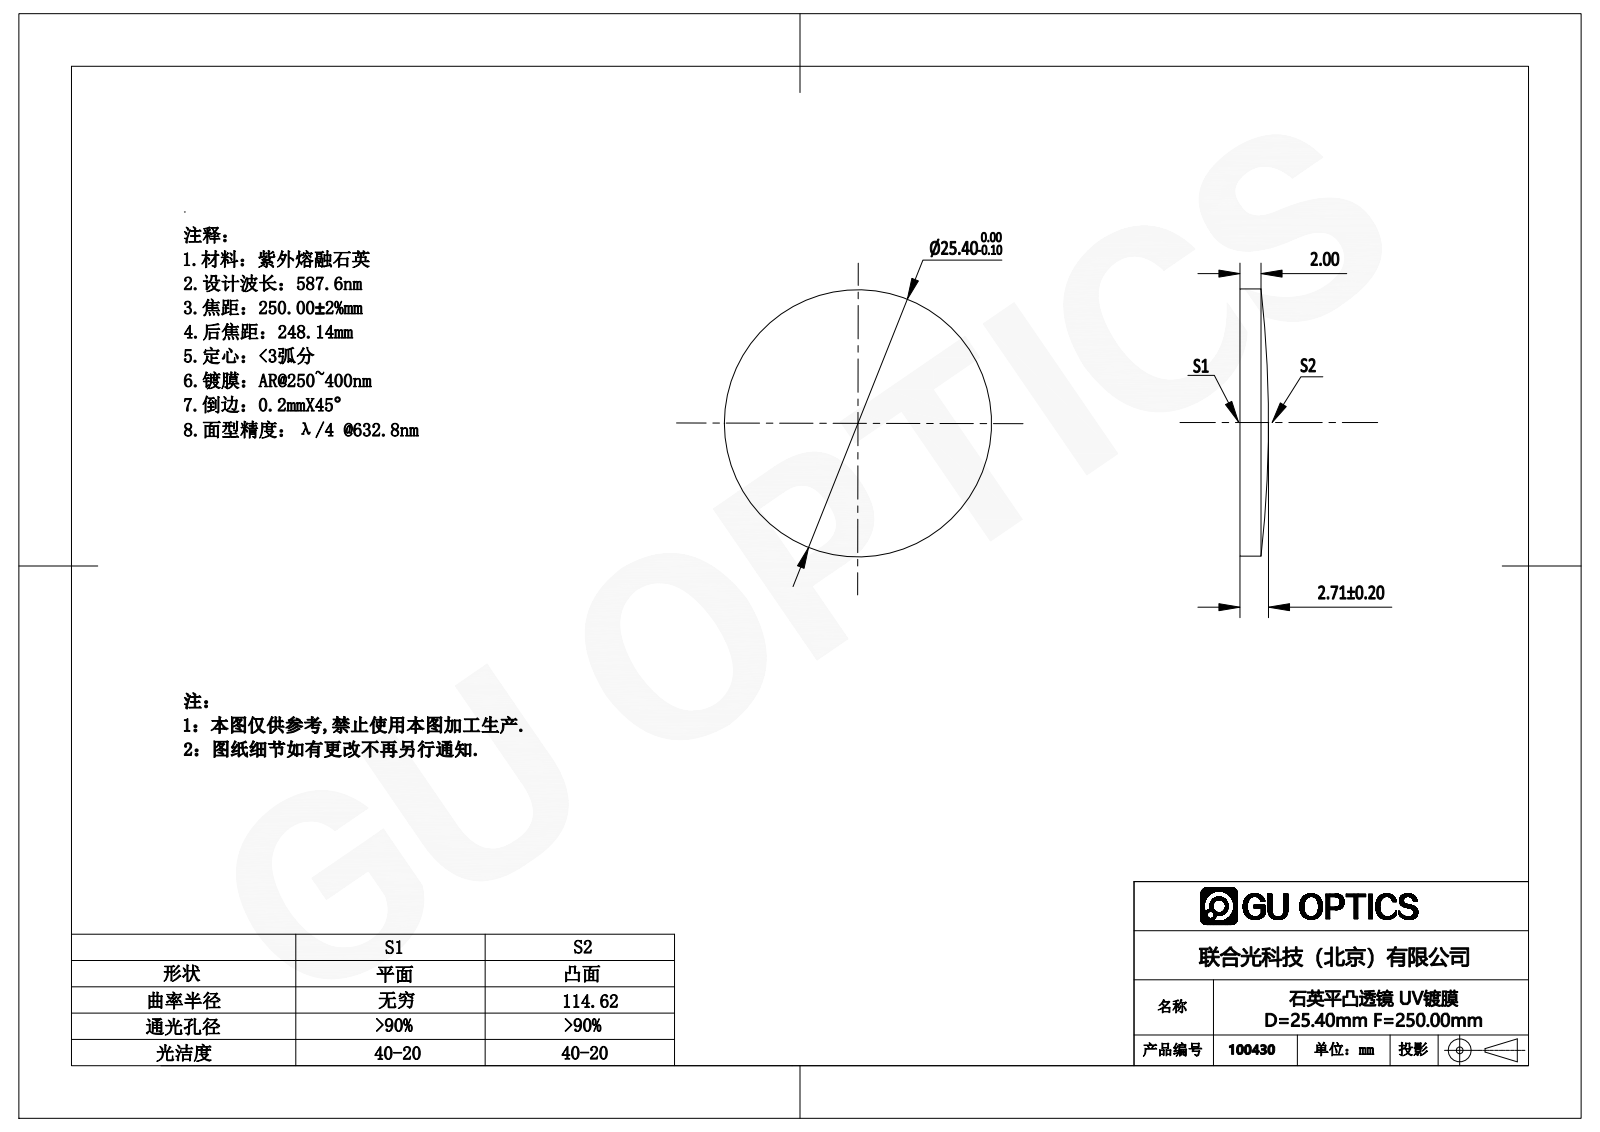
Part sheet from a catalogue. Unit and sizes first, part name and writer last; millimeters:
Units: millimetres
Overall size (bounding box): 25.4 × 25.4 × 2.71
Round bosses / shafts (diameter × count): ⌀25.4 ×1
Volume: 1 193 mm³ · Surface area: 1 175 mm²
Bodies: 1 solid, 5 faces (1 planar, 2 cylindrical, 2 other)
Part name (STEP PRODUCT): 100380
STEP written by: SolidWorks 2016 (AUTOMOTIVE_DESIGN)
